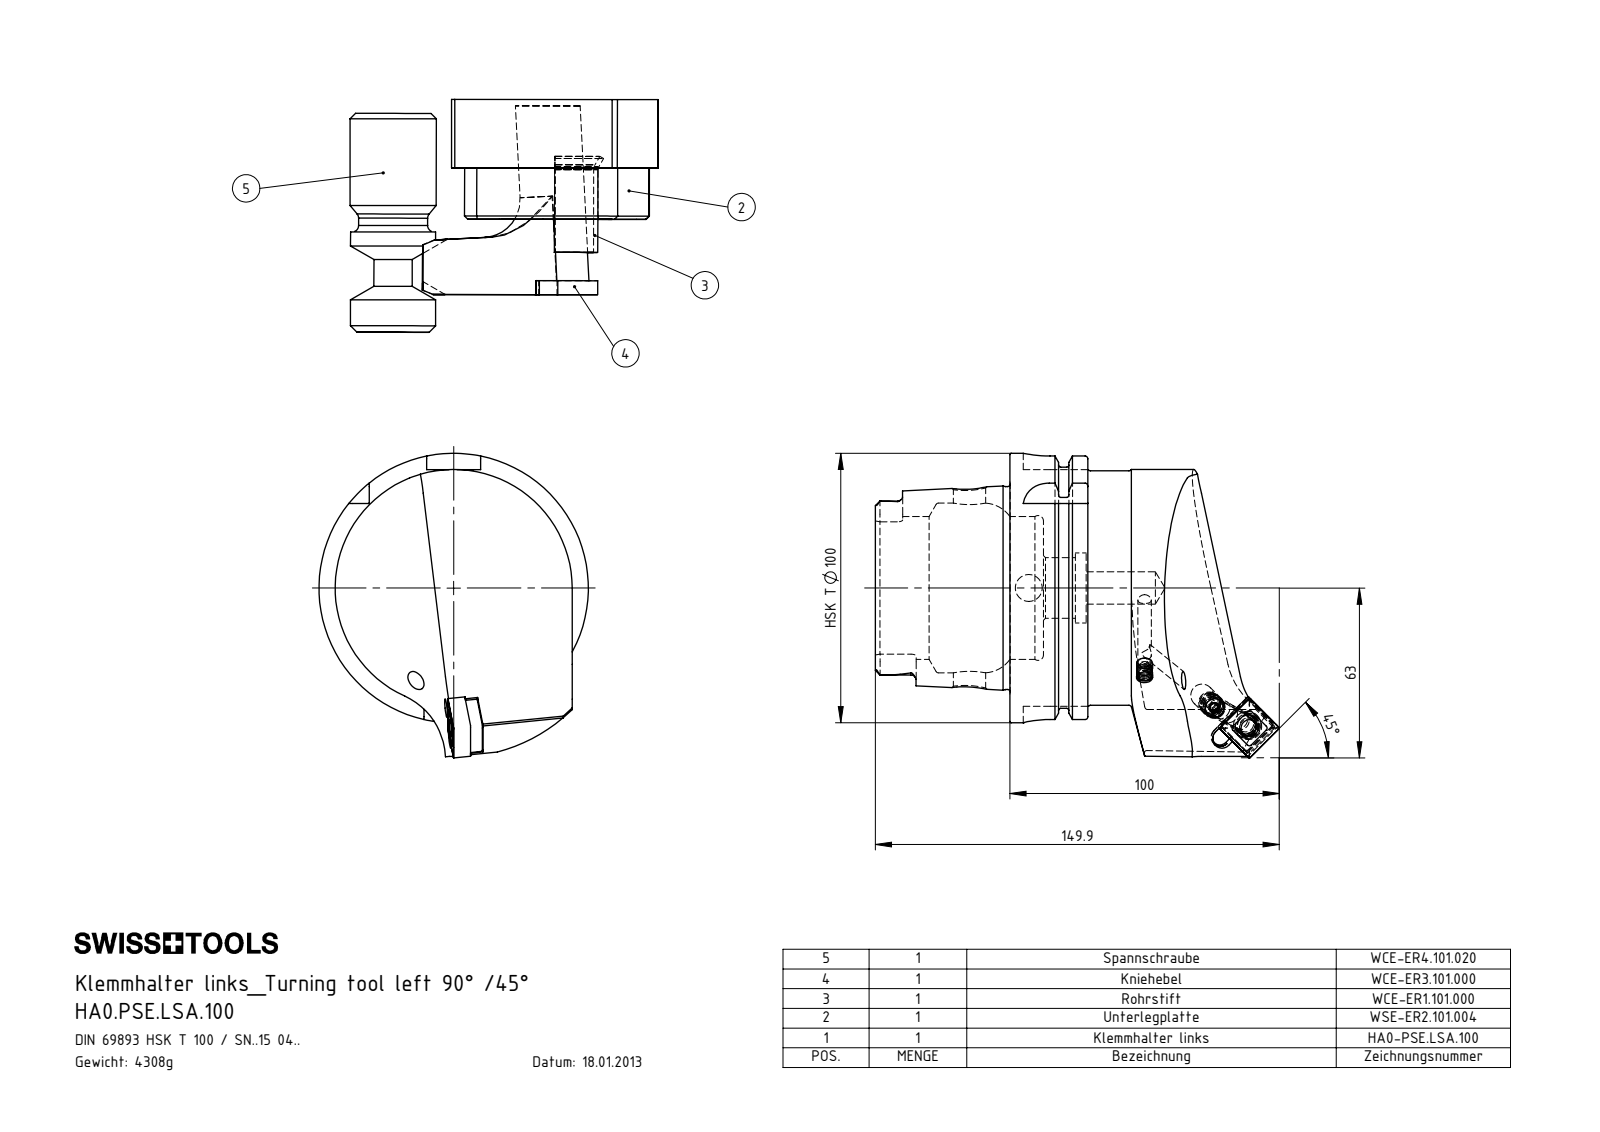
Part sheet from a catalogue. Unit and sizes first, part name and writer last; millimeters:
Units: millimetres
Overall size (bounding box): 149.89 × 113 × 100
Round holes (diameter × count): ⌀5 ×3, ⌀12 ×2, ⌀6 ×1, ⌀6.35 ×1, ⌀7 ×1, ⌀8.05 ×1, ⌀8.4 ×1, ⌀10 ×1, ⌀22.5 ×1, ⌀26 ×1, ⌀53 ×1, ⌀63 ×1
Round bosses / shafts (diameter × count): ⌀6 ×2, ⌀100 ×1, ⌀91.95 ×1, ⌀87 ×1, ⌀75.26 ×1, ⌀8 ×1, ⌀7.9 ×1, ⌀6.4 ×1
Partial cylindrical surfaces — rounded edges, fillets, slot ends (radius × count): R1.9 ×6, R3.5 ×5, R0.4 ×4, R1.5 ×4, R4.88 ×4, R10 ×4, R0.3 ×2, R26 ×2
Main face-to-face distances: 12.45, 16.5, 28.95, 49.9, 62.35, 78.85, 87.8, 78.2, 28.3, 15.85
Hole centre spacings: 15, 15.21
Volume: 546 784 mm³ · Surface area: 72 545 mm²
Bodies: 8 solids, 303 faces (120 planar, 75 cylindrical, 108 other)
Part name (STEP PRODUCT): SNMG150612; WCE-ER4.101.020_A; WCE-ER3.101.000_A; WCE-ER1.101.000 (+4 more)
STEP written by: SolidWorks 2017 (AUTOMOTIVE_DESIGN)
